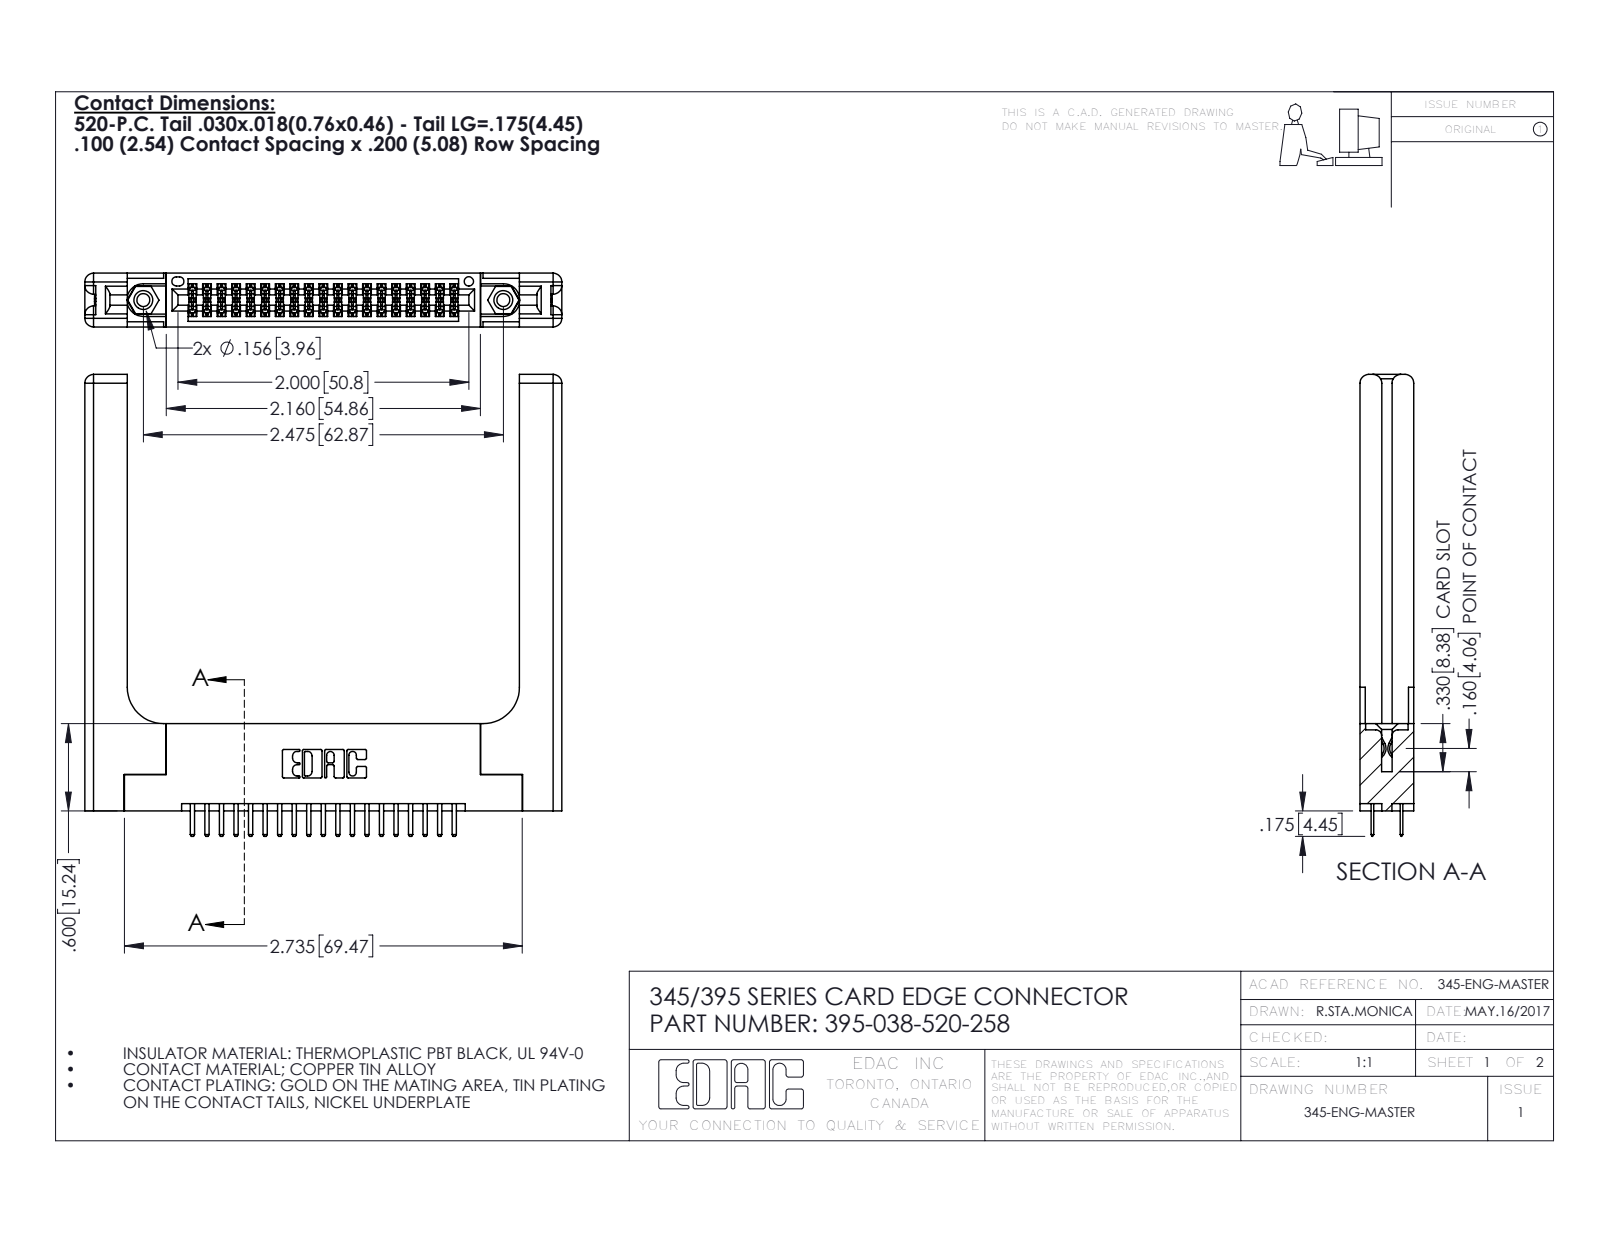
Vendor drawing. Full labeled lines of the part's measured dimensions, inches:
Part name (STEP PRODUCT): 345 Part_Flush Mounting Lugs - 0.156 Dia-TH; 345-250-001_345-250-001-102; 395-038-520-258; 345-292-001_345-293-120 (+1 more)
STEP written by: SolidWorks 2016 (CONFIG_CONTROL_DESIGN)
Units: inches
Bodies: 43 solids, 2434 faces (1558 planar, 816 cylindrical, 60 other)
Overall size (bounding box): 3.279 × 3.175 × 0.37
Volume: 0.997 in³ · Surface area: 25.11 in²
Round holes (diameter × count): ⌀0.089 ×2, ⌀0.125 ×2, ⌀0.156 ×2, ⌀0.064 ×1
Round bosses / shafts (diameter × count): ⌀0.155 ×2
Partial cylindrical surfaces — rounded edges, fillets, slot ends (radius × count): R0.006 ×57, R0.01 ×42, R0.01 ×22, R0.06 ×16, R0.007 ×6, R0.031 ×6, R0.026 ×3, R0.014 ×2
Main face-to-face distances: 0.37, 0.072, 0.298, 0.2, 0.15, 0.148, 0.077, 0.22, 0.098, 0.272
Hole centre spacings: 0.27, 2.241, 2.475
